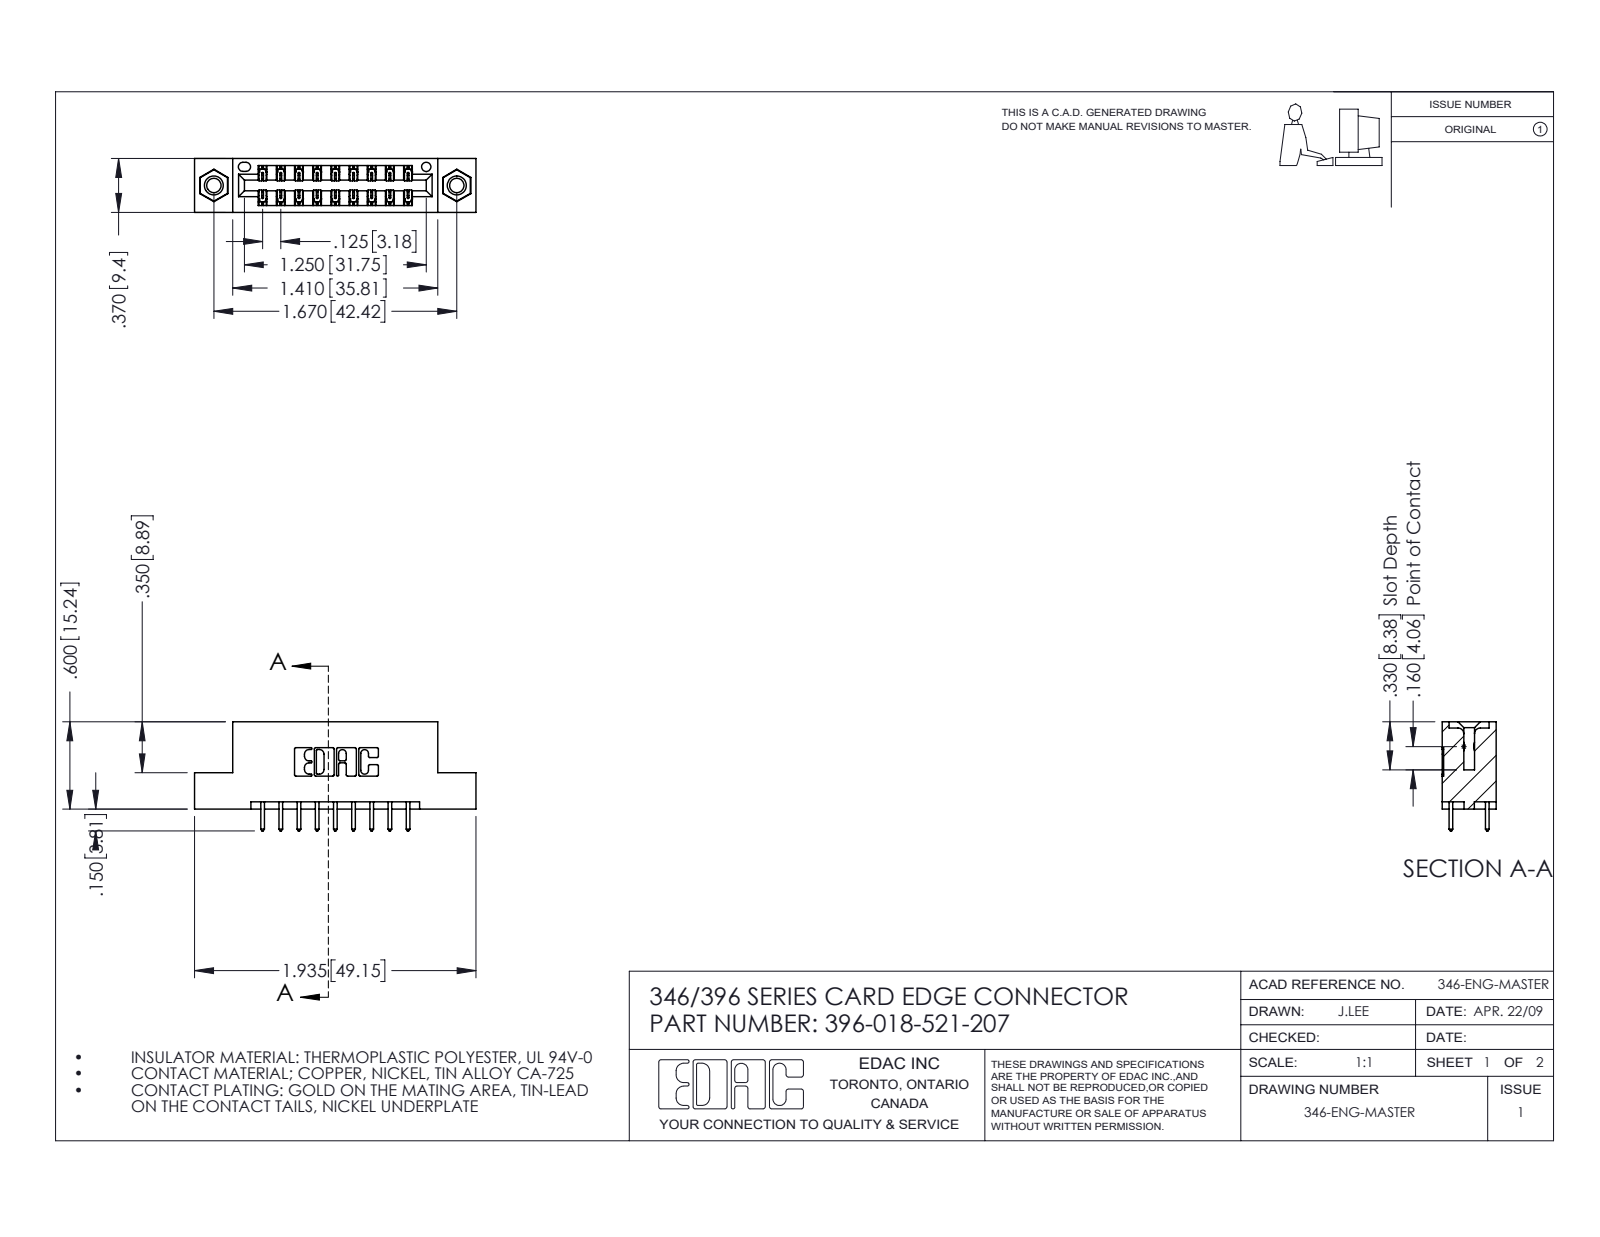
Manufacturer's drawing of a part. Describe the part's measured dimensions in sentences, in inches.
The part is named "345-250-001_345-250-005-103; 396-018-521-207; 345-292-001_345-293-121; 346 Part_Flush Mounting Lugs - 0.156 Dia-TI". Its 3-D file was written by "SolidWorks 2016 (CONFIG_CONTROL_DESIGN)". It is 21 solids with 1118 faces: 738 planar, 364 cylindrical and 16 other. Overall it measures 1.935 by 0.75 by 0.37 inches. Its volume is 0.276 cubic inches and its surface area 8.792 square inches. Round holes: 2 of diameter 0.098, 2 of diameter 0.125, 2 of diameter 0.156, 1 of diameter 0.064. Round bosses or shafts: 2 of diameter 0.155. Partial cylindrical surfaces (rounded edges, fillets, slot ends): 27 of radius 0.006, 22 of radius 0.01, 18 of radius 0.01, 6 of radius 0.007, 6 of radius 0.031, 3 of radius 0.026, 2 of radius 0.014, 2 of radius 0.022. The main face-to-face distances are 0.25, 0.048, 0.322, 0.37, 0.072, 0.298, 0.025, 0.275, 0.148, 0.222. The hole center spacings are 0.246, 1.465, 1.67.
